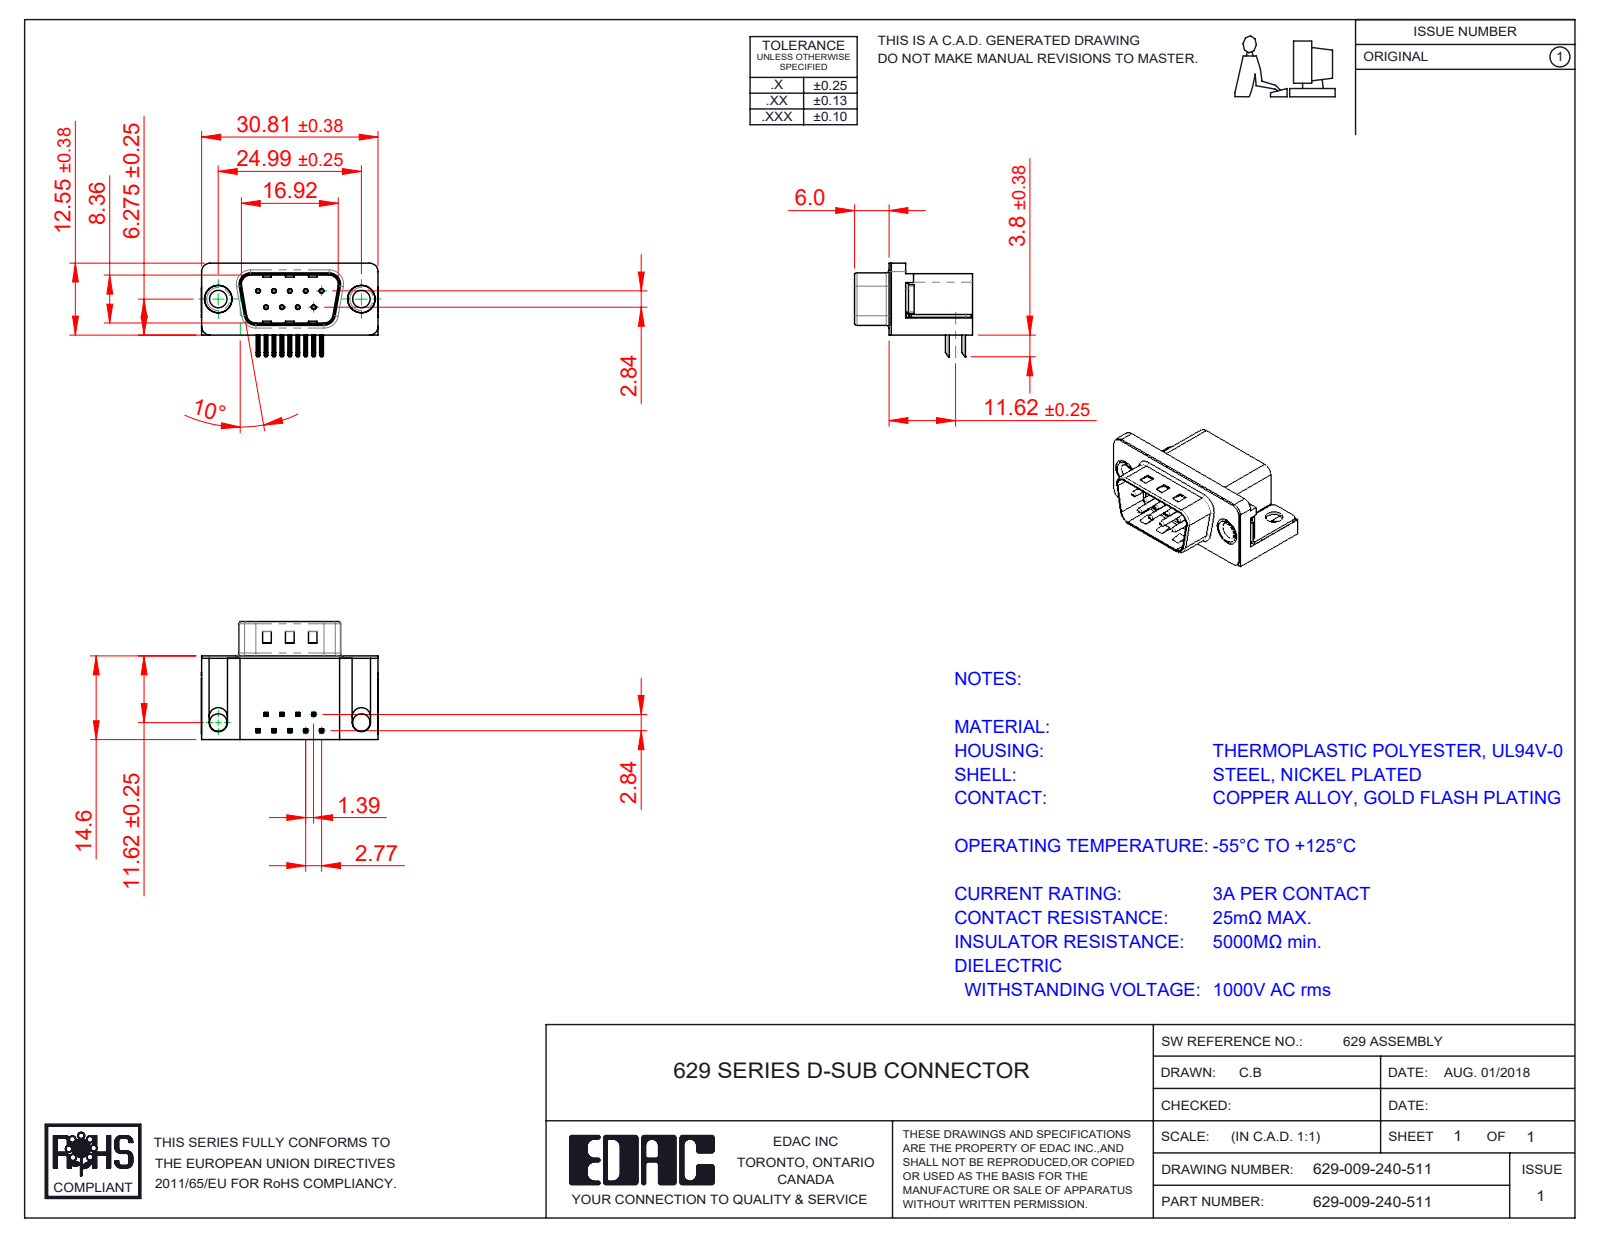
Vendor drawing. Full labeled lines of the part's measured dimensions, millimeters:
Part name (STEP PRODUCT): 629-009-240-511; 629 Thru Hole Board Mount; 629 Housing_09 Socket; 629 Contact Bottom (+3 more)
STEP written by: SolidWorks 2020 (CONFIG_CONTROL_DESIGN)
Units: millimetres
Bodies: 15 solids, 949 faces (571 planar, 297 cylindrical, 81 other)
Overall size (bounding box): 30.89 × 20.6 × 16.35
Volume: 3 704 mm³ · Surface area: 4 703 mm²
Round holes (diameter × count): ⌀0.35 ×9, ⌀0.8 ×9, ⌀3.05 ×4, ⌀4 ×2, ⌀4.8 ×2, ⌀5 ×2
Round bosses / shafts (diameter × count): ⌀0.75 ×9, ⌀4.9 ×2, ⌀4.75 ×2, ⌀3.85 ×2
Partial cylindrical surfaces — rounded edges, fillets, slot ends (radius × count): R0.25 ×44, R0.12 ×18, R1 ×16, R0.5 ×9, R1.5 ×8, R1.6 ×8, R0.9 ×4, R2 ×4
Main face-to-face distances: 0.4, 14.2, 10.35, 14.6, 0.5, 2.9, 11.7, 2.5, 2.1, 6.7
Hole centre spacings: 3.16, 2.77, 5.54, 5.03, 5.04, 8.31, 7.48, 7.49
